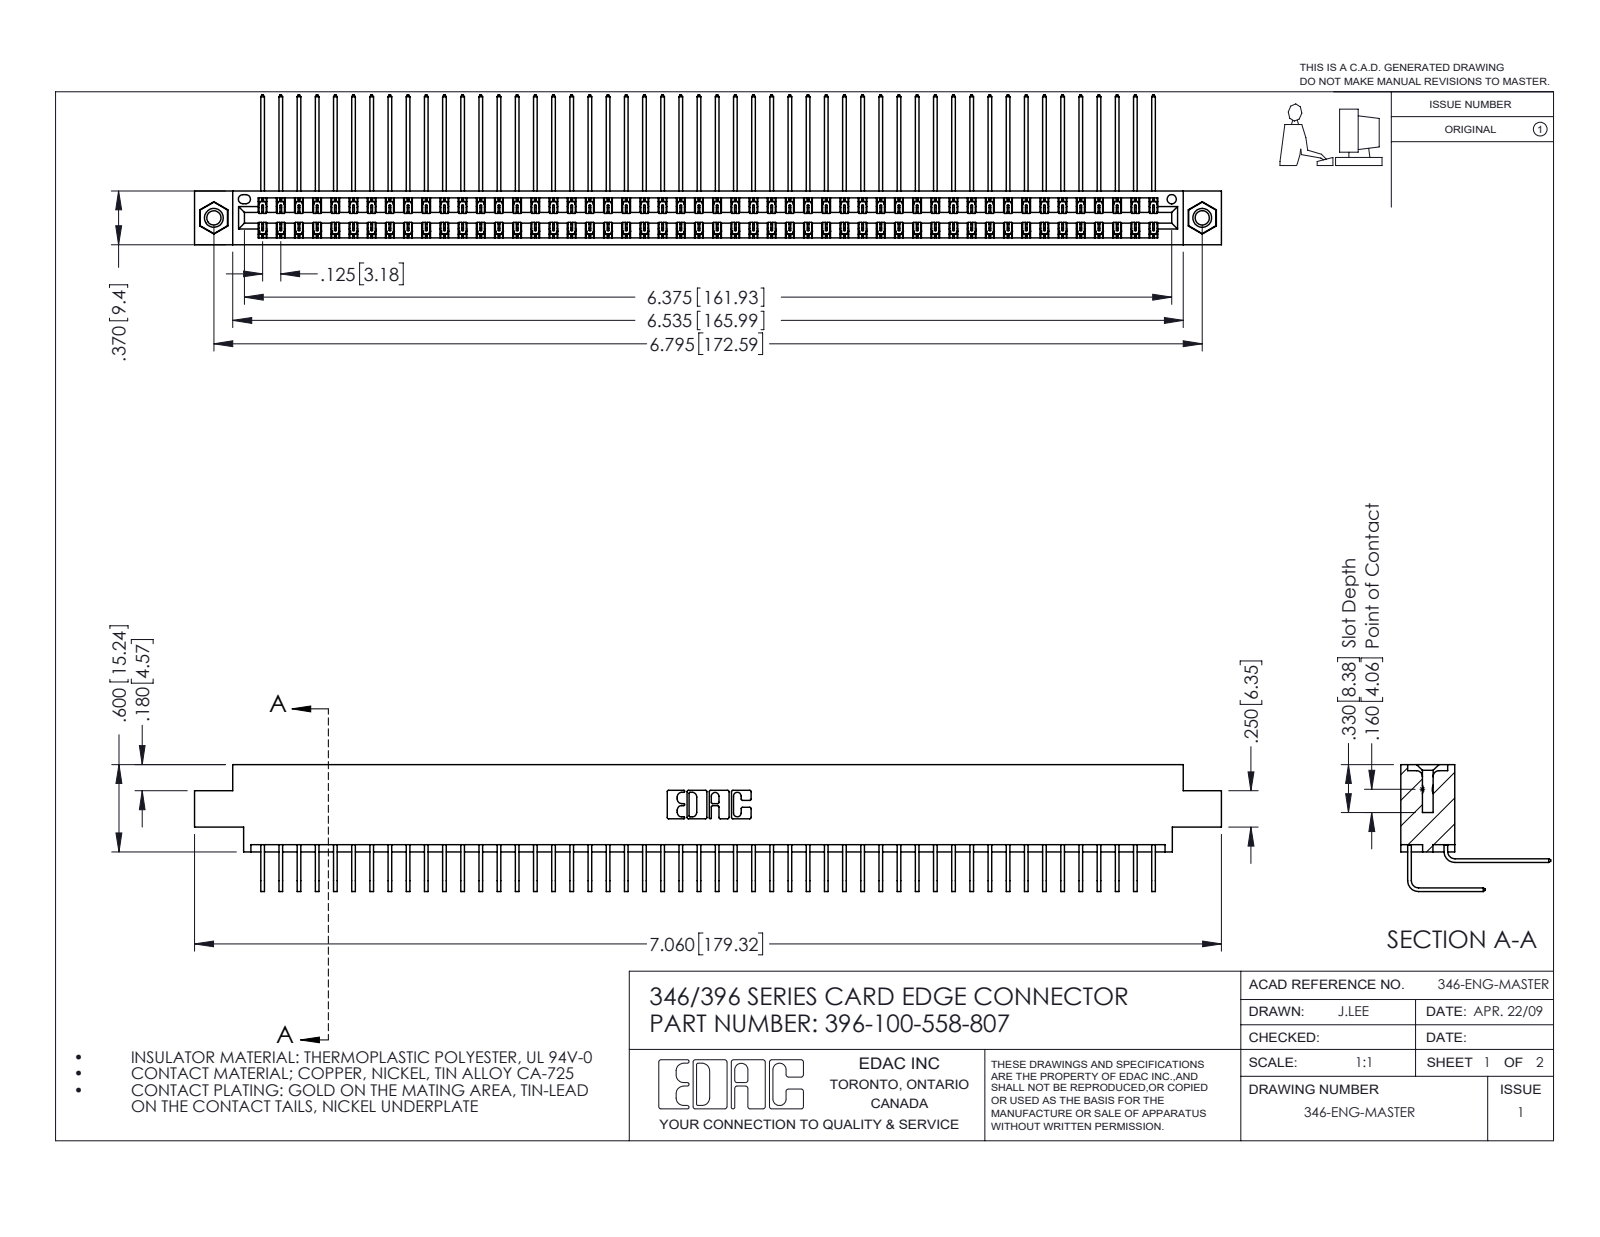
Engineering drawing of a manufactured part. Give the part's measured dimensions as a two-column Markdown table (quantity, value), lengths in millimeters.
| quantity | value |
| --- | --- |
| part name | 345-250-001_345-250-005-103; 345-292-001_558 559 Tail - 1; 396-100-558-807; 345-292-001_558 Tail - 2 (+1 more) |
| STEP written by | SolidWorks 2016 (CONFIG_CONTROL_DESIGN) |
| units | millimeters |
| bodies | 103 solids, 5586 faces (3812 planar, 1758 cylindrical, 16 other) |
| overall size | 179.3 × 26.2 × 22.2 |
| volume | 17 960 mm³ |
| surface area | 27 790 mm² |
| round holes (diameter × count) | 2.5 × 2, 3.2 × 2, 4 × 2, 1.6 × 1 |
| round bosses / shafts (diameter × count) | 3.9 × 2 |
| partial cylindrical surfaces (radius × count) | 0.2 × 150, 0.3 × 22, 0.2 × 6, 0.8 × 6, 0.7 × 3, 0.4 × 2, 0.6 × 2, 0.6 × 2 |
| main face-to-face distances | 8.2, 1.2, 0.6, 9.4, 6.4, 7.6, 1.8, 7, 5.6, 3.8 |
| hole center spacings | 6.2, 167.3, 172.6 |
